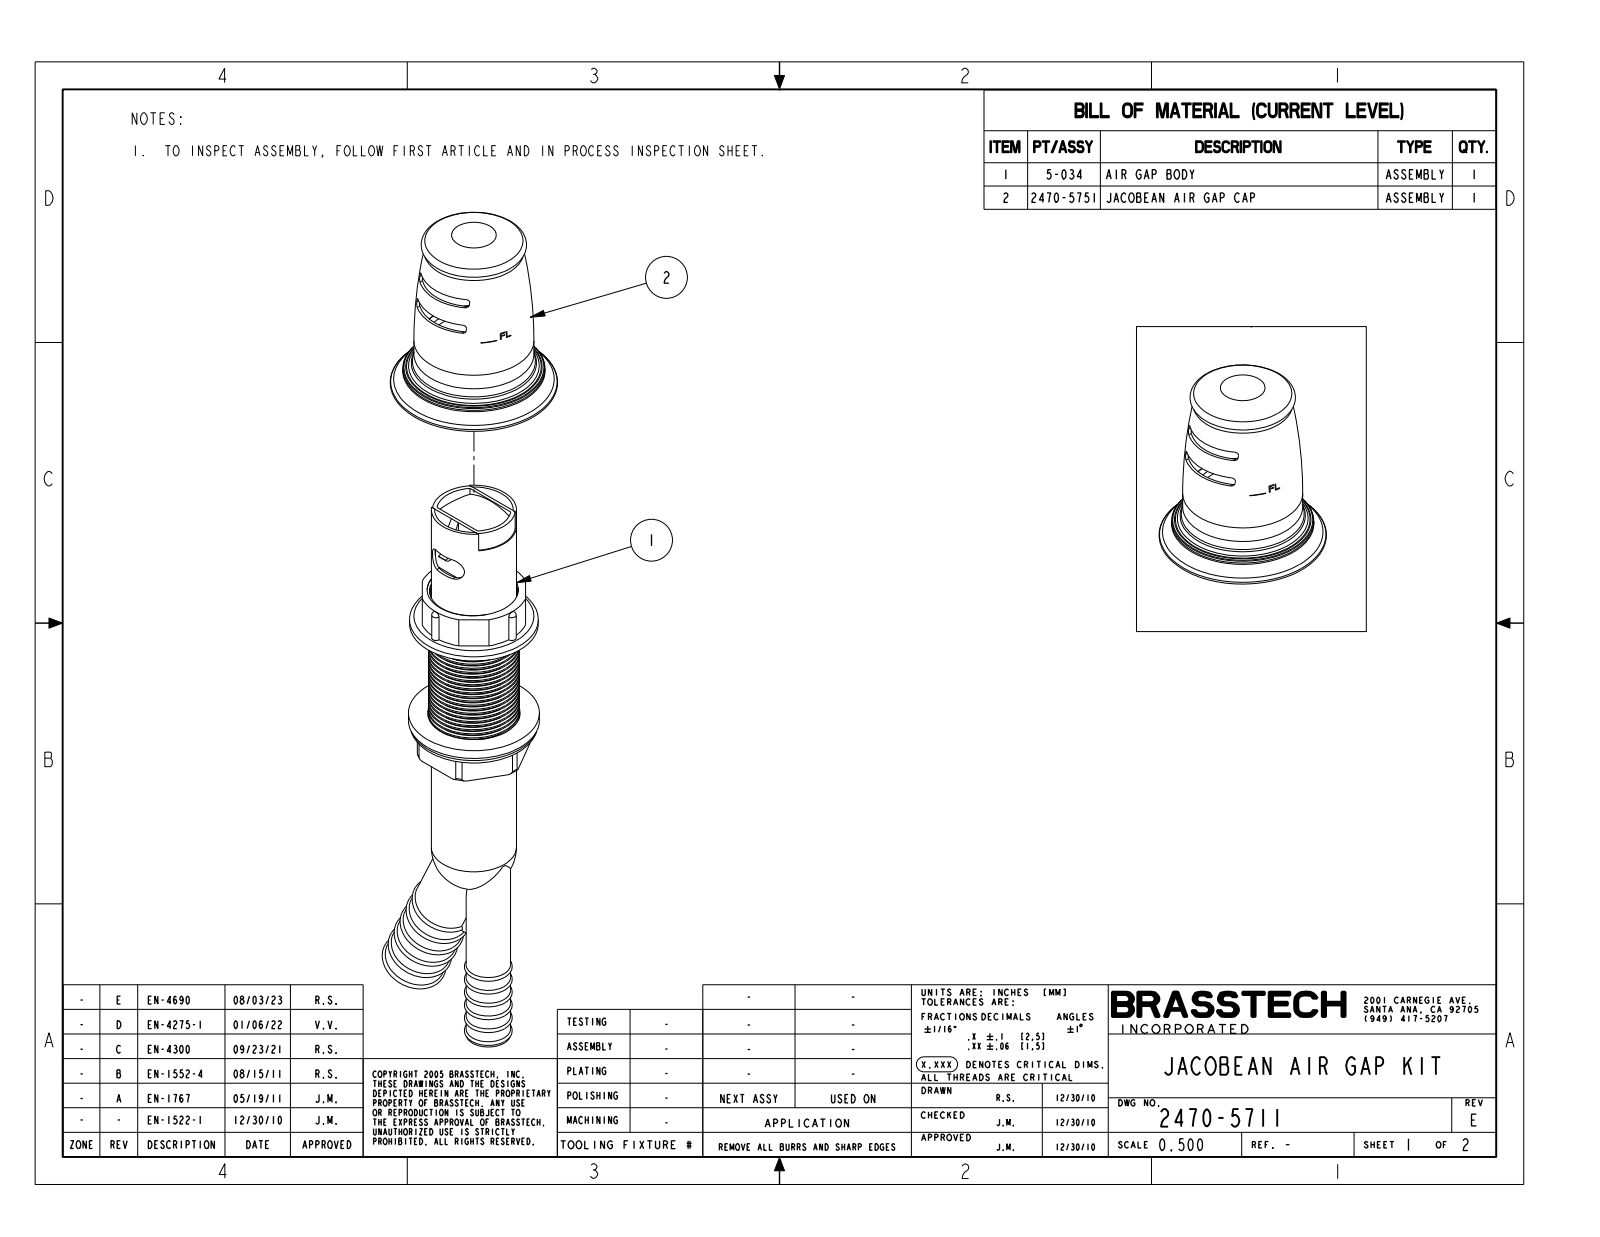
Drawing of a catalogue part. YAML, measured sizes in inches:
part_name: "2470-5711"
step_written_by: "CREO PARAMETRIC BY PTC INC, 2018400 (AUTOMOTIVE_DESIGN)"
units: inches
bodies: {solids: 1, faces: 291, planar: 66, cylindrical: 132, other: 93}
overall_size: [9.368, 2.582, 2]
volume: 10.43
surface_area: 74.73
round_holes:
  - {diameter: 1.2, count: 1}
  - {diameter: 1.27, count: 1}
  - {diameter: 1.28, count: 1}
round_bosses_or_shafts:
  - {diameter: 1.8, count: 1}
  - {diameter: 1.76, count: 1}
  - {diameter: 1.65, count: 1}
  - {diameter: 1.259, count: 1}
  - {diameter: 1.17, count: 1}
  - {diameter: 0.854, count: 1}
  - {diameter: 0.61, count: 1}
partial_cylinders:
  - {radius: 0.04, count: 6}
  - {radius: 0.049, count: 5}
  - {radius: 0.05, count: 3}
  - {radius: 0.157, count: 2}
face_to_face_distances: [1.5, 2.275, 0.775, 3.14, 1.64, 0.865, 1.42, 0.345, 1.075, 0.61]
